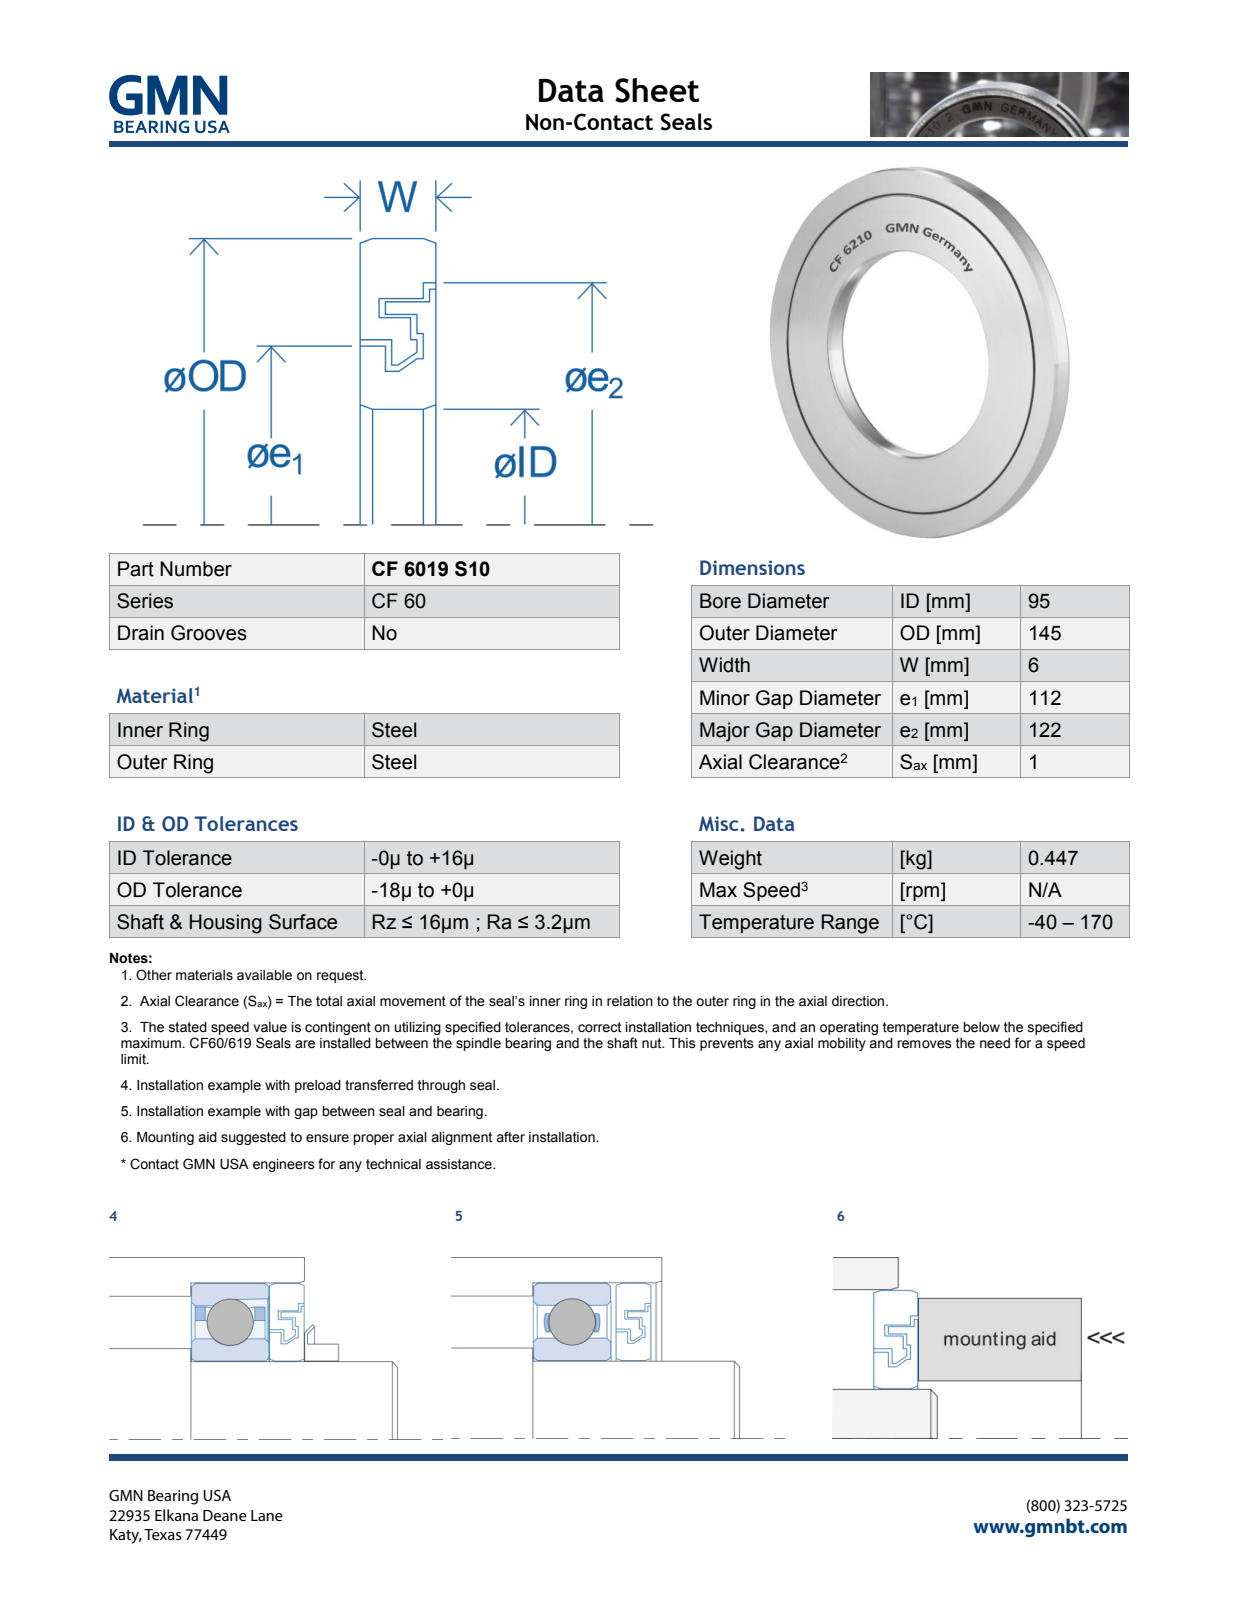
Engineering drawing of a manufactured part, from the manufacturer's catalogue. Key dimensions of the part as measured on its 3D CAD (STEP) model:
Part name (STEP PRODUCT): CF6019S10_PRT
STEP written by: PRO/ENGINEER BY PARAMETRIC TECHNOLOGY CORPORATION, 2013150 (AUTOMOTIVE_DESIGN)
Units: millimetres
Bodies: 2 solids, 669 faces (627 planar, 30 cylindrical, 12 other)
Overall size (bounding box): 145 × 145 × 6.05
Volume: 53 310 mm³ · Surface area: 36 863 mm²
Round holes (diameter × count): ⌀95 ×1, ⌀109 ×1, ⌀113 ×1, ⌀114 ×1, ⌀117 ×1, ⌀119.5 ×1, ⌀122 ×1
Round bosses / shafts (diameter × count): ⌀145 ×1, ⌀121 ×1, ⌀119 ×1, ⌀116.5 ×1, ⌀112 ×1, ⌀110 ×1, ⌀108 ×1
Main face-to-face distances: 6, 0.5, 2, 2.5, 1, 1.5, 4, 3, 3.5, 4.5
